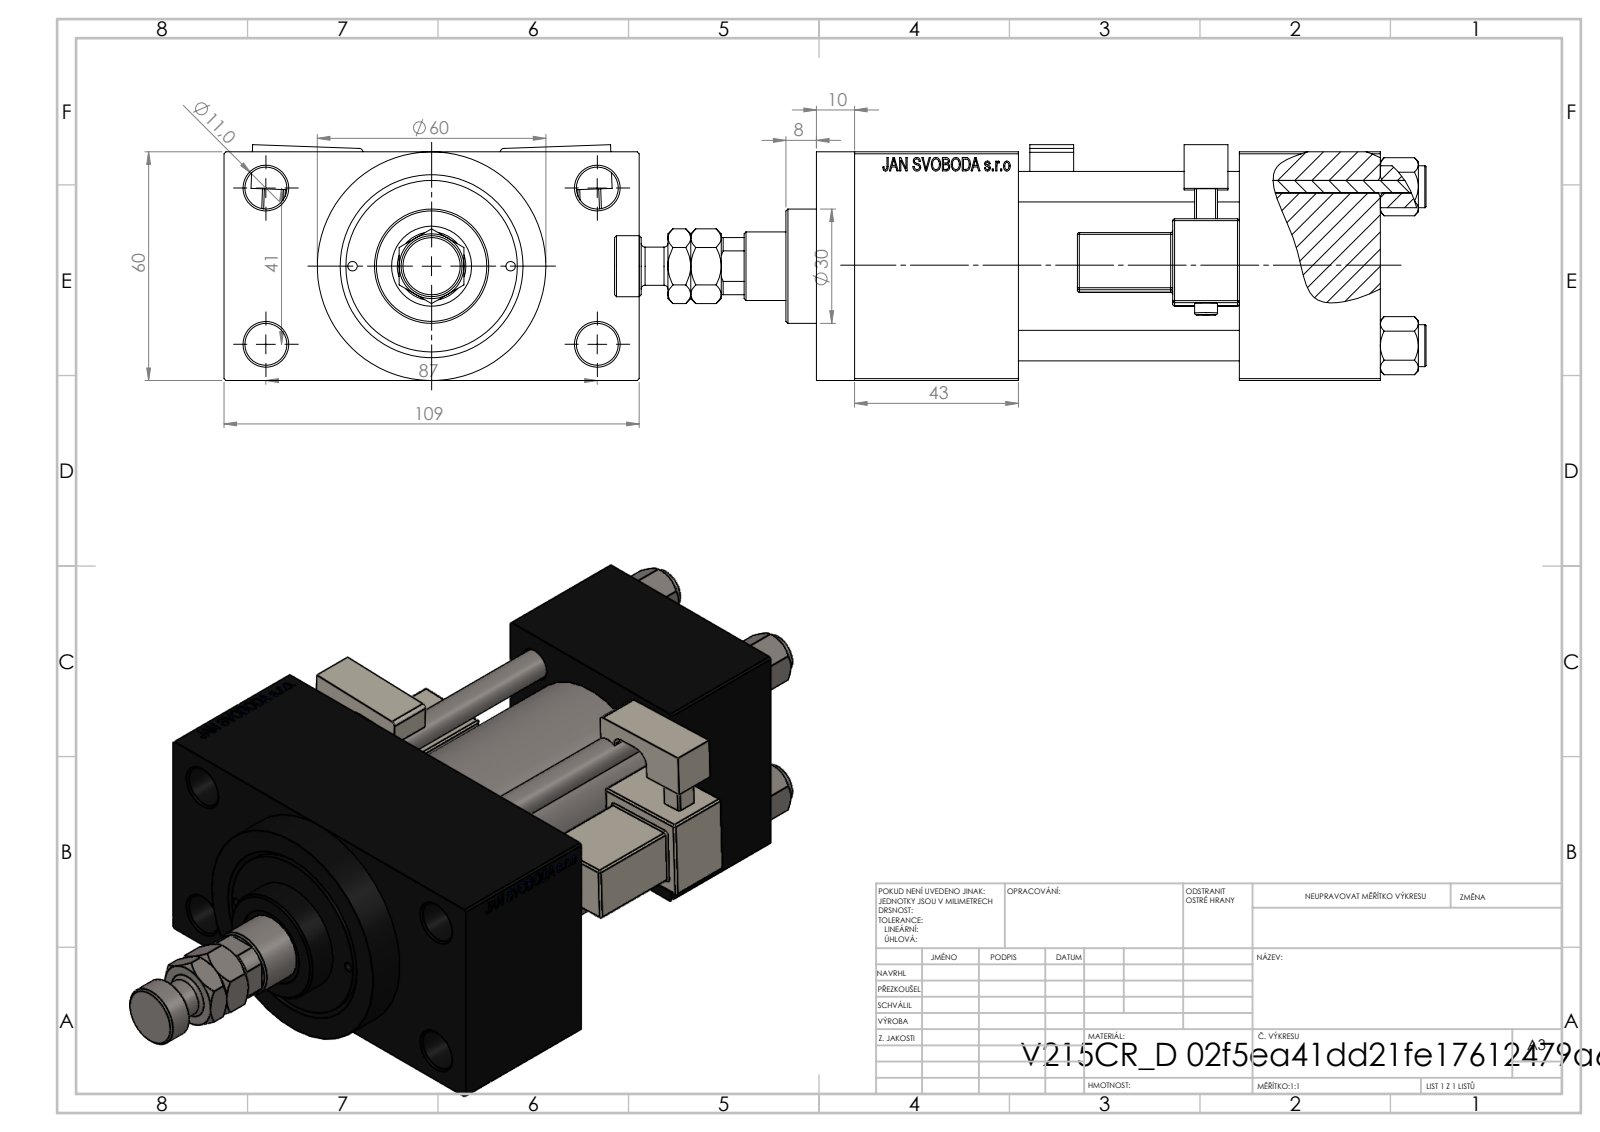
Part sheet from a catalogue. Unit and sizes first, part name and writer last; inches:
Units: inches
Overall size (bounding box): 8.386 × 4.291 × 2.437
Round holes (diameter × count): ⌀0.315 ×4, ⌀0.433 ×4, ⌀0.098 ×2, ⌀0.276 ×2, ⌀0.656 ×2, ⌀0.945 ×2, ⌀0.335 ×1, ⌀0.709 ×1, ⌀0.827 ×1, ⌀1.22 ×1, ⌀1.575 ×1, ⌀1.772 ×1
Round bosses / shafts (diameter × count): ⌀0.433 ×4, ⌀0.236 ×2, ⌀2.362 ×1, ⌀1.811 ×1, ⌀1.181 ×1, ⌀0.63 ×1, ⌀0.394 ×1
Partial cylindrical surfaces — rounded edges, fillets, slot ends (radius × count): R0.02 ×48, R0.039 ×2, R0.098 ×2, R0.157 ×2, R0.335 ×1
Main face-to-face distances: 2.362, 2.283, 0.965, 3.327, 1.457, 3.74, 5.433, 3.976, 1.693, 4.291
Hole centre spacings: 0.821, 0.892, 1.161, 1.206, 1.642, 1.832, 1.856, 1.893
Volume: 34.09 in³ · Surface area: 211.8 in²
Bodies: 14 solids, 1318 faces (574 planar, 156 cylindrical, 588 other)
Part name (STEP PRODUCT): NUT_M5_D; V215CR_D_Body; V215CR_MSU; MFA (+3 more)
STEP written by: SolidWorks 2019 (CONFIG_CONTROL_DESIGN)
